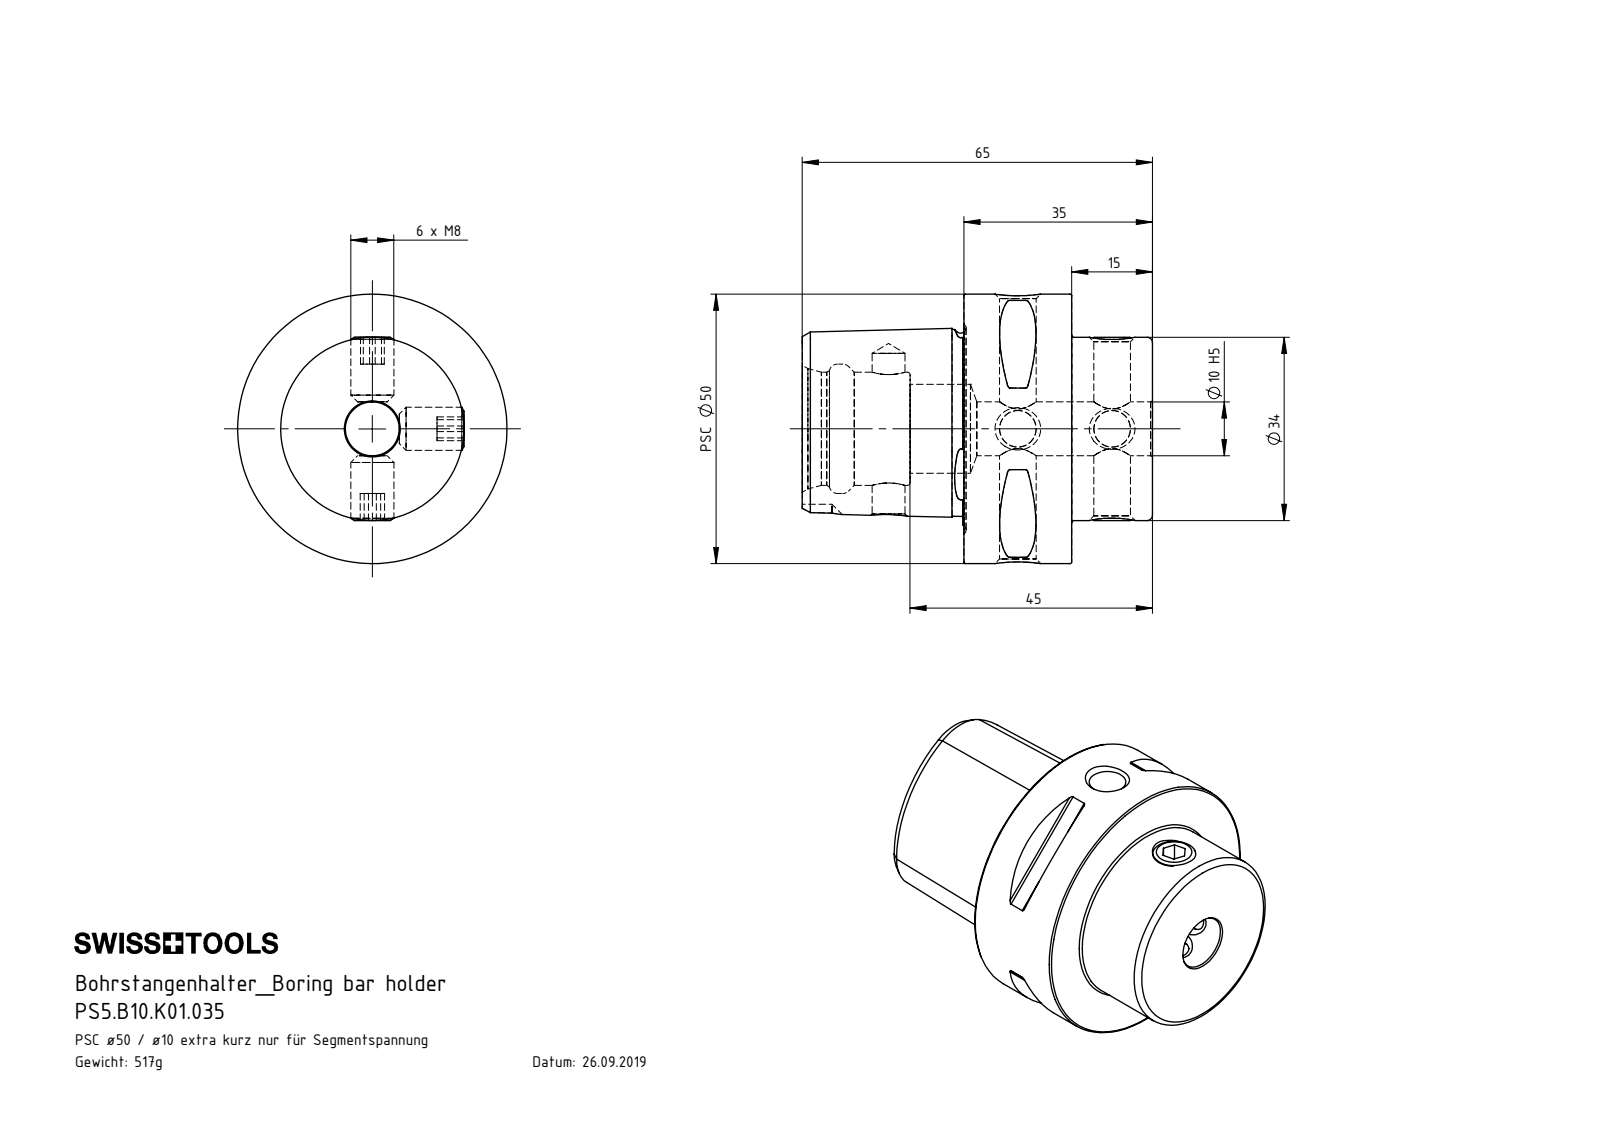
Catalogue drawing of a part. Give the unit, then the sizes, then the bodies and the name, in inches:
Units: inches
Overall size (bounding box): 2.559 × 1.969 × 1.969
Round holes (diameter × count): ⌀0.268 ×4, ⌀0.24 ×1, ⌀0.394 ×1, ⌀0.65 ×1, ⌀0.827 ×1, ⌀0.945 ×1
Round bosses / shafts (diameter × count): ⌀0.315 ×4, ⌀1.969 ×1, ⌀1.339 ×1
Partial cylindrical surfaces — rounded edges, fillets, slot ends (radius × count): R0.02 ×8, R0.157 ×1
Main face-to-face distances: 0.787, 0.591, 1.378, 1.181, 1.969, 2.559, 0.157, 0.755, 0.394, 1.748
Hole centre spacings: 0.689, 0.945, 1.634
Volume: 4.019 in³ · Surface area: 29.63 in²
Bodies: 7 solids, 171 faces (74 planar, 30 cylindrical, 67 other)
Part name (STEP PRODUCT): ISO 4026 - M8 x 12_PreviewCfg; PS5-B10.K01.035_A; PS5.B10.K01.035
STEP written by: SolidWorks 2017 (AUTOMOTIVE_DESIGN)
